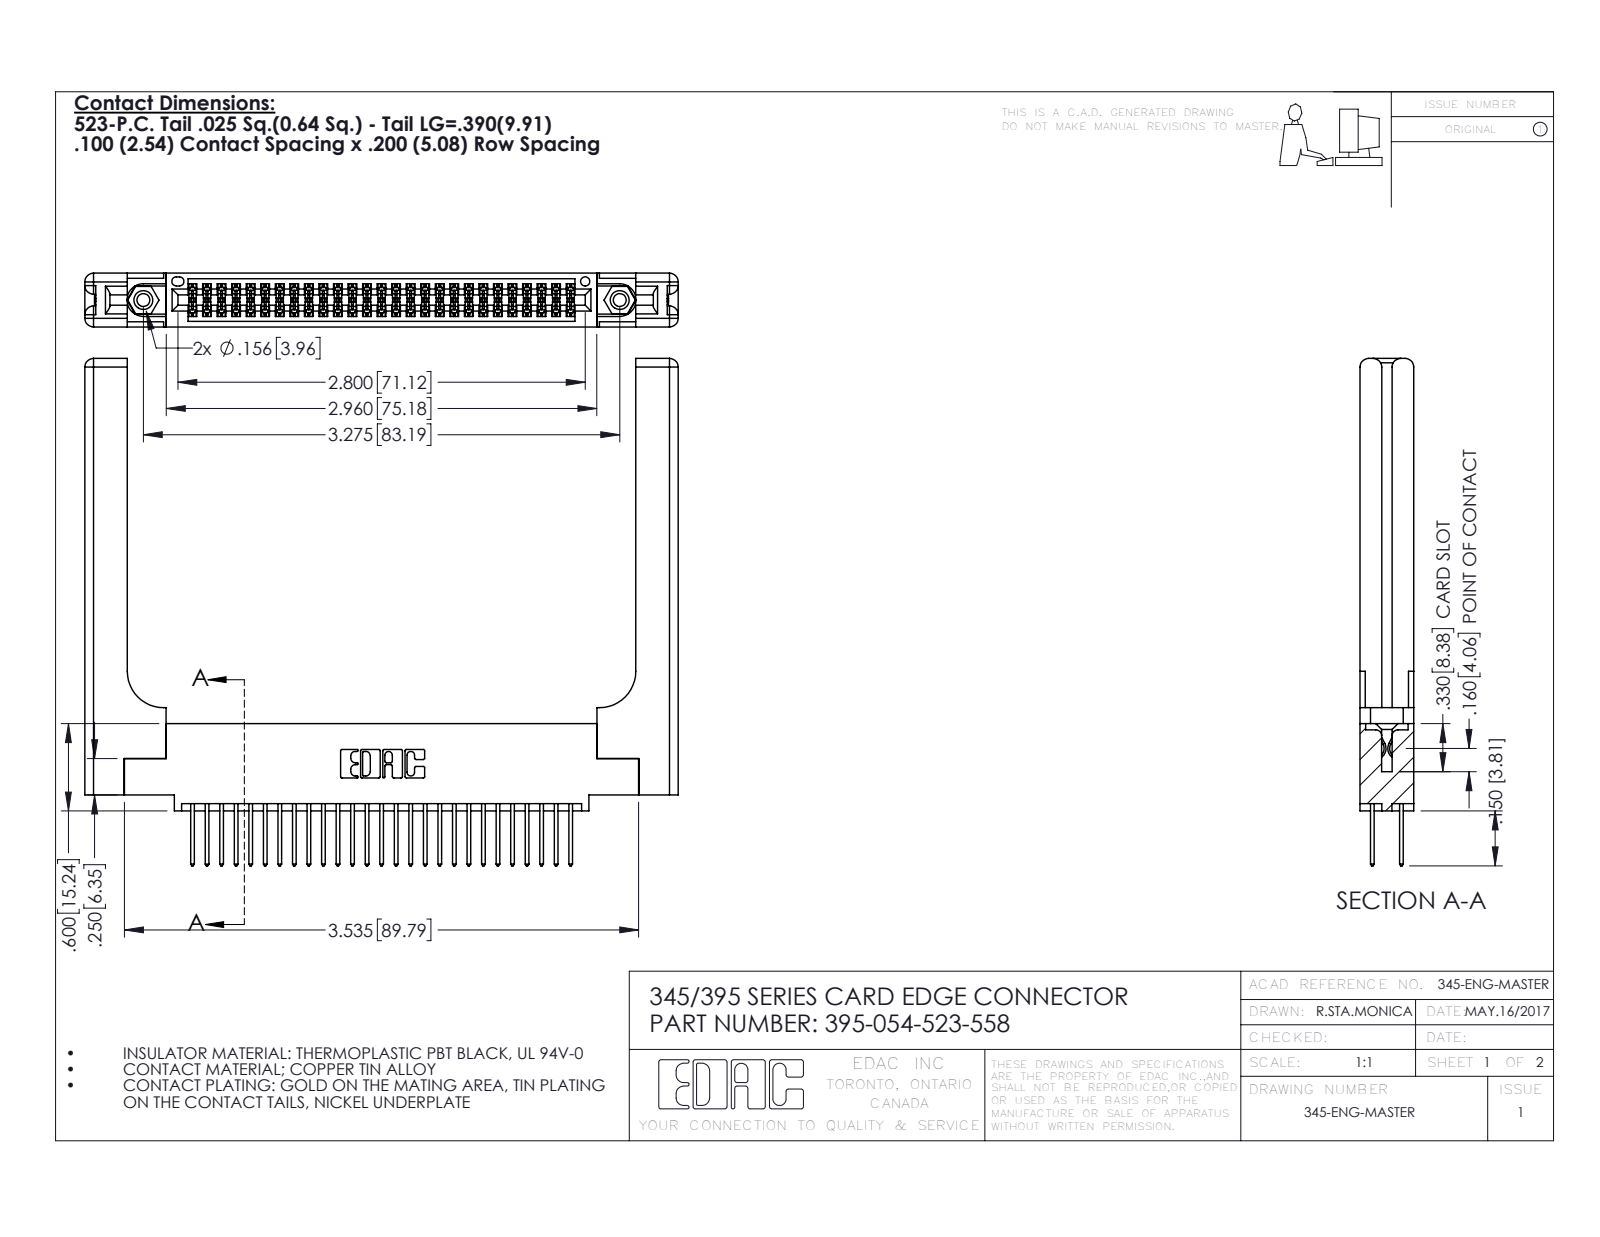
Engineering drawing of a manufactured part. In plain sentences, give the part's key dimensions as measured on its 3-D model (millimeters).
The part is named "395-054-523-558; 345-250-001_345-250-001-102; 345 Part_0.110 Offset - 0.156 Dia-TH; 345-292-001_345-293-123 (+1 more)". Its 3-D file was written by "SolidWorks 2016 (CONFIG_CONTROL_DESIGN)". It is 59 solids with 3086 faces: 2014 planar, 1012 cylindrical and 60 other. Overall it measures 103.6 by 88.6 by 9.4 millimeters. Its volume is 18 440 cubic millimeters and its surface area 20 080 square millimeters. Round holes: 2 of diameter 2.3, 2 of diameter 3.2, 2 of diameter 4, 1 of diameter 1.6. Round bosses or shafts: 2 of diameter 3.9. Partial cylindrical surfaces (rounded edges, fillets, slot ends): 81 of radius 0.2, 54 of radius 0.3, 22 of radius 0.3, 16 of radius 1.5, 6 of radius 0.2, 6 of radius 0.8, 3 of radius 0.7, 2 of radius 0.4. The main face-to-face distances are 1.8, 9.4, 7.6, 2.5, 6.9, 0.6, 5.1, 5.7, 3.8, 3.8. The hole center spacings are 6.9, 77.2, 83.2.
